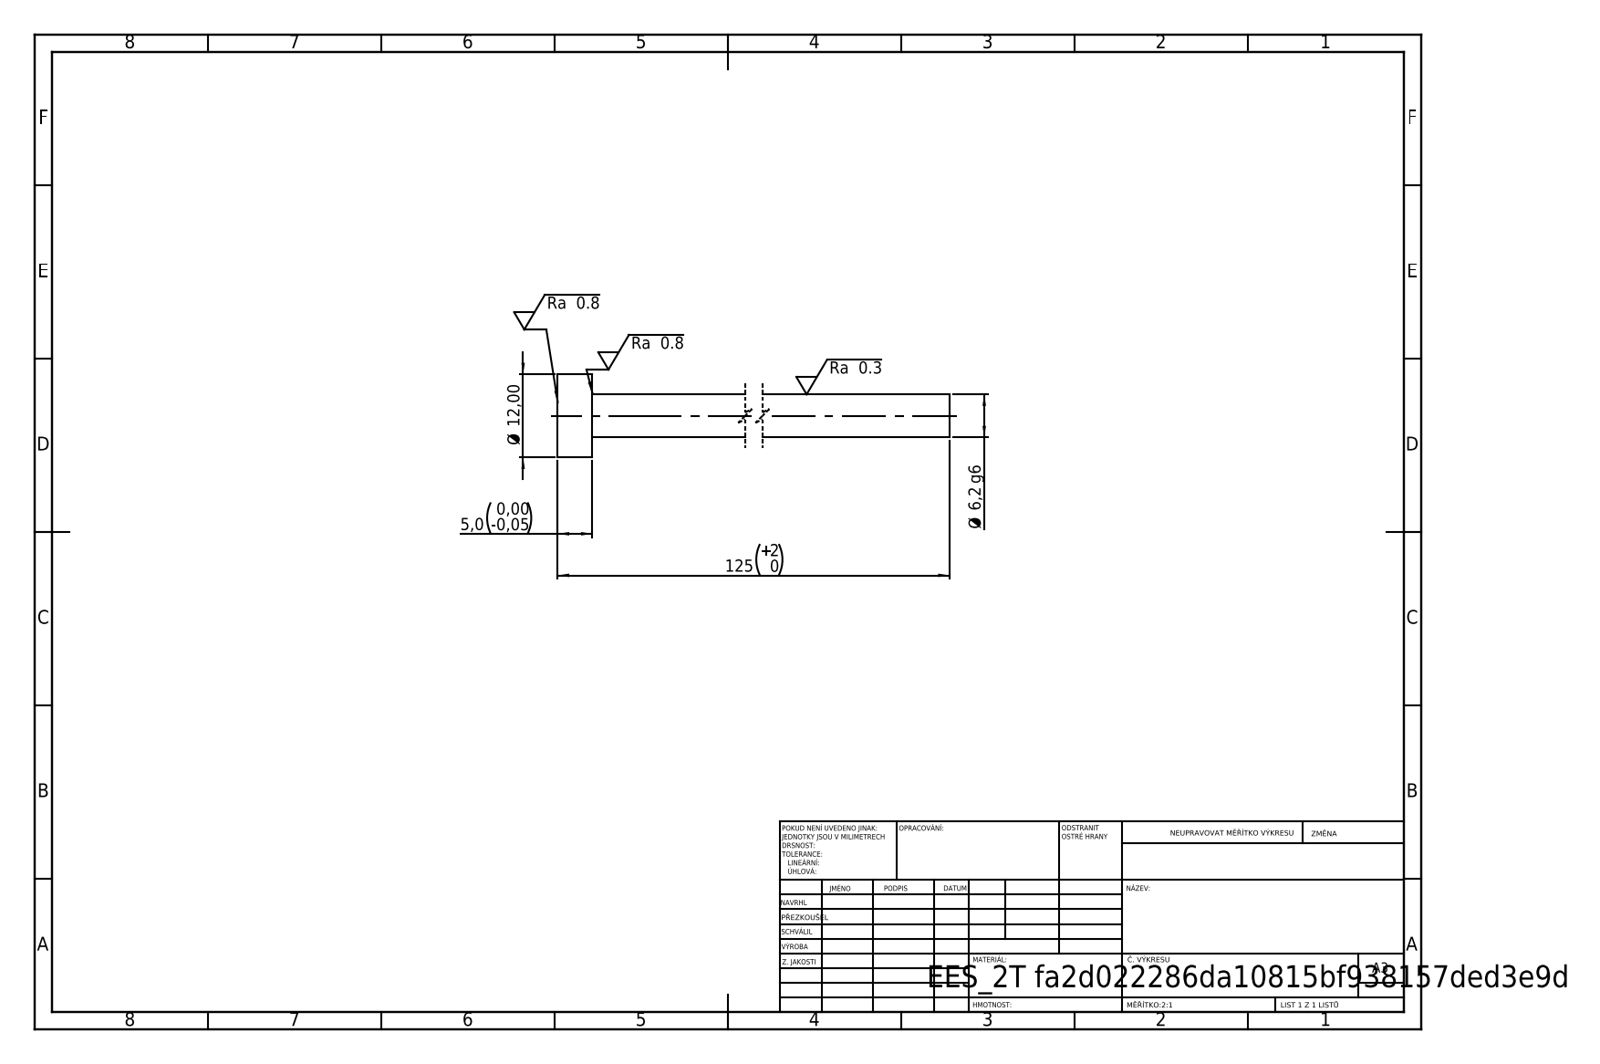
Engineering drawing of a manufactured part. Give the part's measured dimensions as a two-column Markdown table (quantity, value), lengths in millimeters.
| quantity | value |
| --- | --- |
| STEP written by | SolidWorks 2019 (CONFIG_CONTROL_DESIGN) |
| units | millimeters |
| bodies | 1 solid, 7 faces (3 planar, 4 cylindrical, 0 other) |
| overall size | 125 × 12 × 12 |
| volume | 4 188 mm³ |
| surface area | 2 752 mm² |
| round bosses / shafts (diameter × count) | 12 × 1, 6.2 × 1 |
| main face-to-face distances | 5, 125, 120 |
